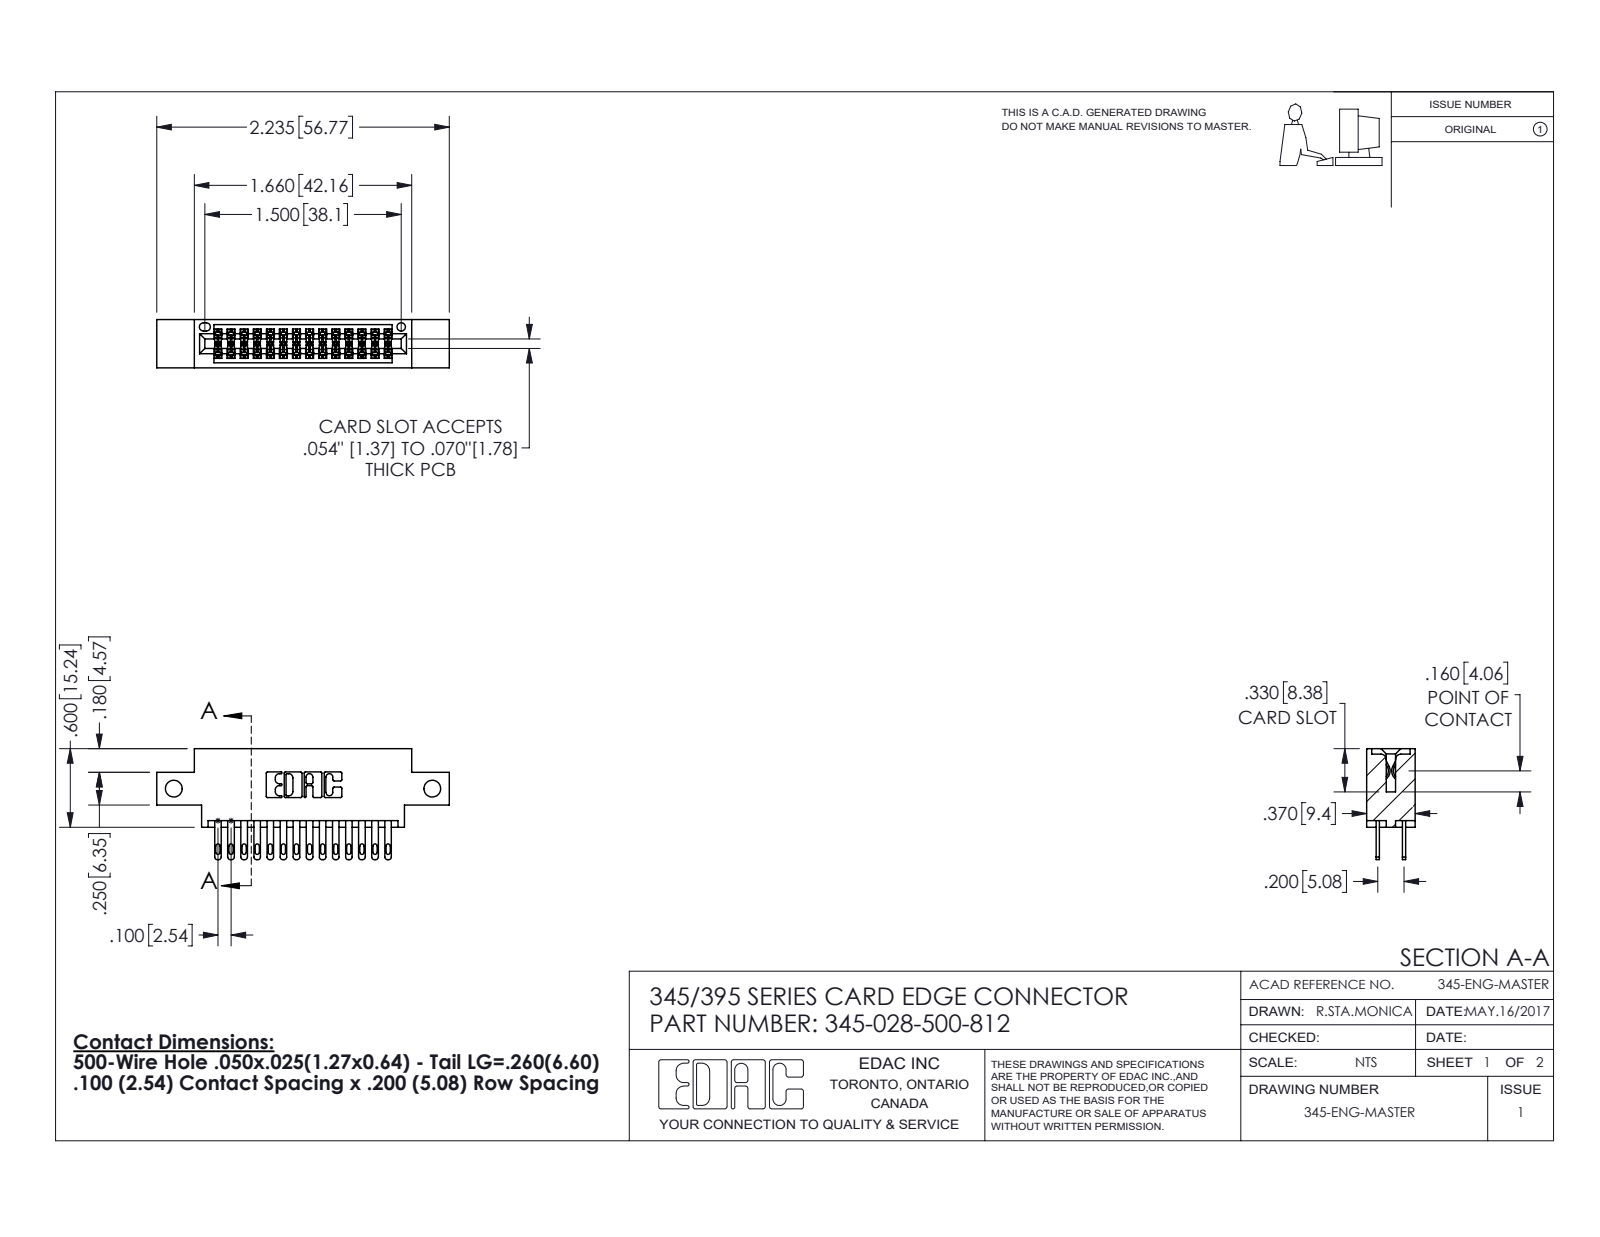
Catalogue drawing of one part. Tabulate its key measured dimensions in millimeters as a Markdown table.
| quantity | value |
| --- | --- |
| part name | 345-292-001_345-293-100; 345 Part_0.170 Offset - Side Mount; 345-028-500-812 |
| STEP written by | SolidWorks 2016 (CONFIG_CONTROL_DESIGN) |
| units | millimeters |
| bodies | 29 solids, 1418 faces (840 planar, 578 cylindrical, 0 other) |
| overall size | 56.8 × 21.5 × 9.4 |
| volume | 5 150 mm³ |
| surface area | 7 348 mm² |
| round holes (diameter × count) | 3.3 × 2, 1.6 × 1 |
| partial cylindrical surfaces (radius × count) | 0.2 × 42, 0.4 × 28, 0.5 × 28, 0.3 × 22, 0.2 × 6, 0.8 × 6, 0.7 × 3, 0.4 × 2 |
| main face-to-face distances | 7.6, 1.8, 5.1, 9.4, 2.5, 6.9, 0.6, 5.7, 4.4, 2.5 |
| hole center spacings | 50.2 |
